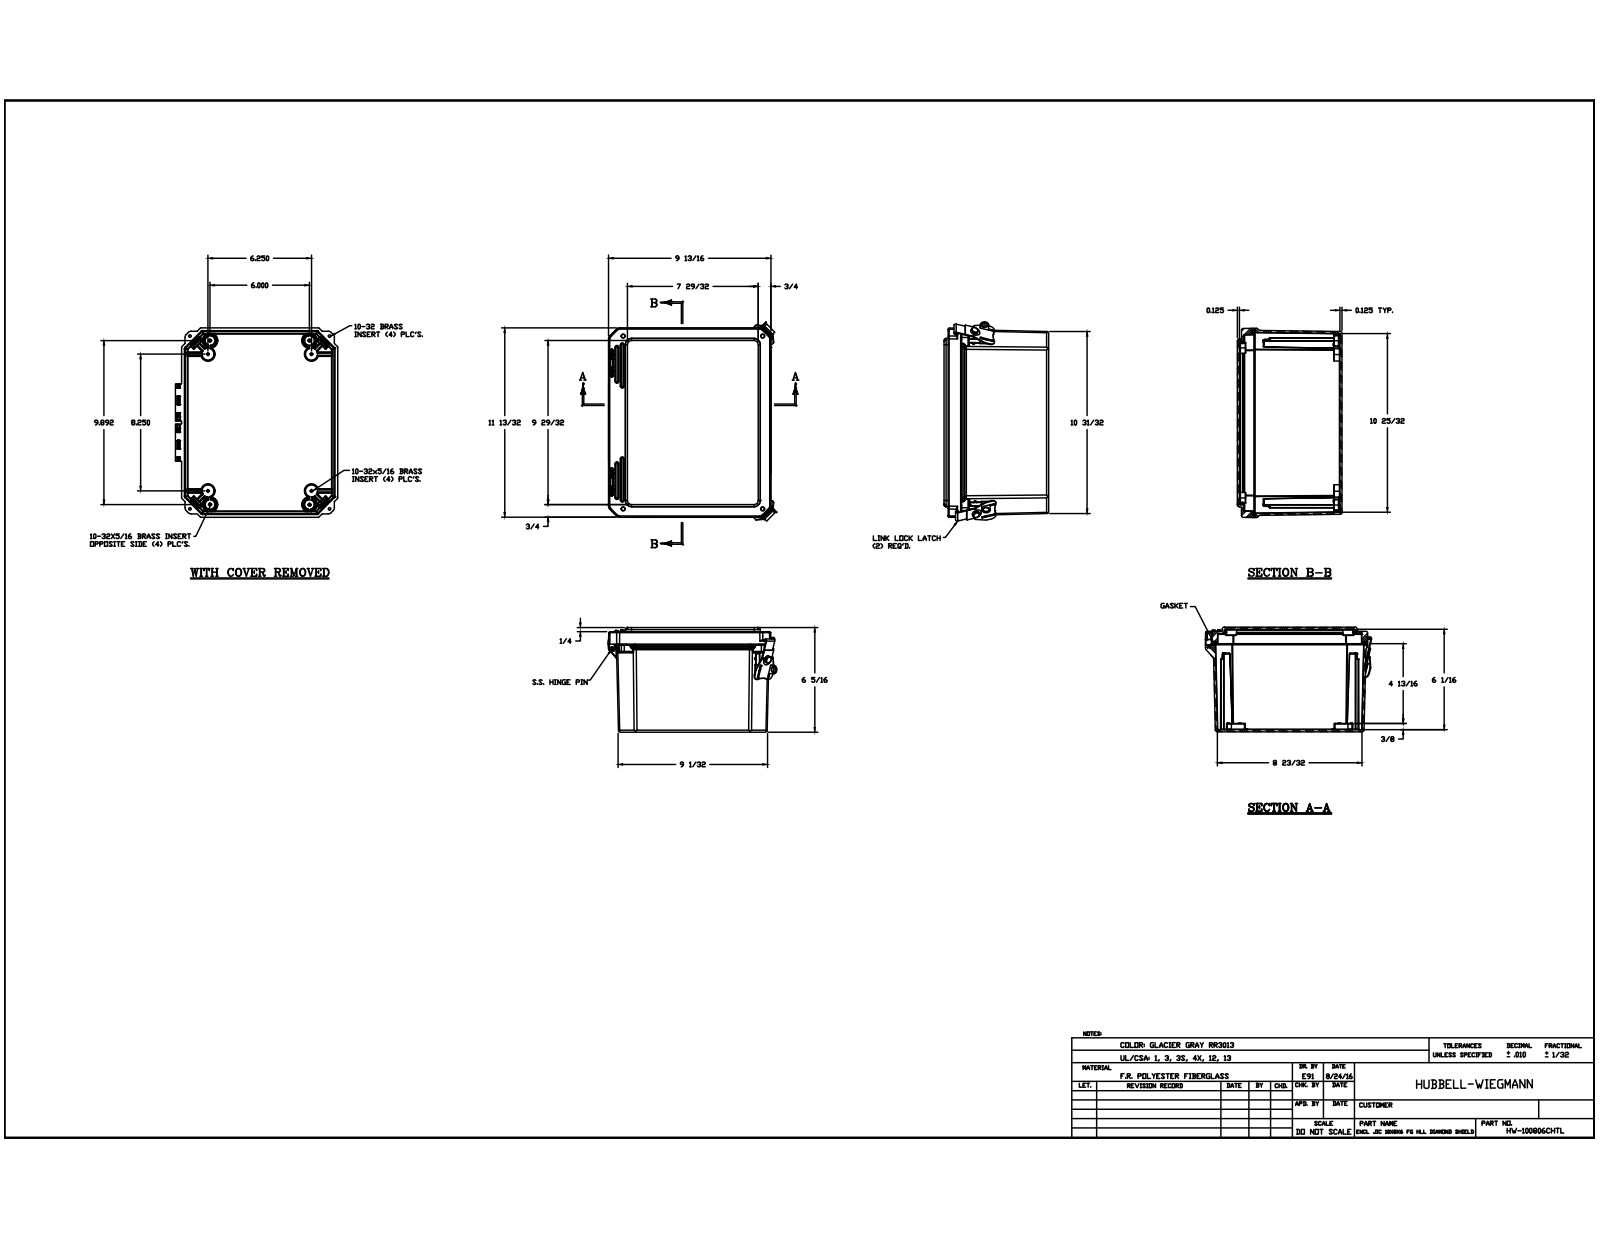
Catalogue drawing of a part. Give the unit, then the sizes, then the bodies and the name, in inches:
Units: inches
Overall size (bounding box): 12.339 × 10.256 × 6.31
Round holes (diameter × count): ⌀0.156 ×16, ⌀0.152 ×8, ⌀0.098 ×4, ⌀0.15 ×4, ⌀0.252 ×4, ⌀0.253 ×4, ⌀0.05 ×2, ⌀0.12 ×2, ⌀0.219 ×2, ⌀0.227 ×2, ⌀0.313 ×2, ⌀0.363 ×2
Round bosses / shafts (diameter × count): ⌀0.246 ×16, ⌀0.87 ×4, ⌀0.209 ×4, ⌀0.2 ×4, ⌀0.135 ×3, ⌀0.05 ×3, ⌀0.6 ×2, ⌀0.435 ×2
Partial cylindrical surfaces — rounded edges, fillets, slot ends (radius × count): R0.01 ×177, R0.005 ×80, R0.02 ×57, R0.03 ×43, R0.125 ×34, R0.039 ×28, R0.063 ×26, R0.03 ×24
Main face-to-face distances: 0.125, 6.185, 0.127, 0.126, 6.31, 6.061, 0.25, 5.935, 0.125, 6.06
Hole centre spacings: 7.416, 11.874, 0.83, 6.18, 9.072, 9.399, 1.24, 1.536
Volume: 71.34 in³ · Surface area: 1 015 in²
Bodies: 35 solids, 2259 faces (755 planar, 892 cylindrical, 612 other)
Part name (STEP PRODUCT): HW-100806CHTL; DS100806BOX; BRASS INSERT-(; BRASS INSERT-(_1 (+7 more)
STEP written by: Autodesk Inventor 2017 (CONFIG_CONTROL_DESIGN)
